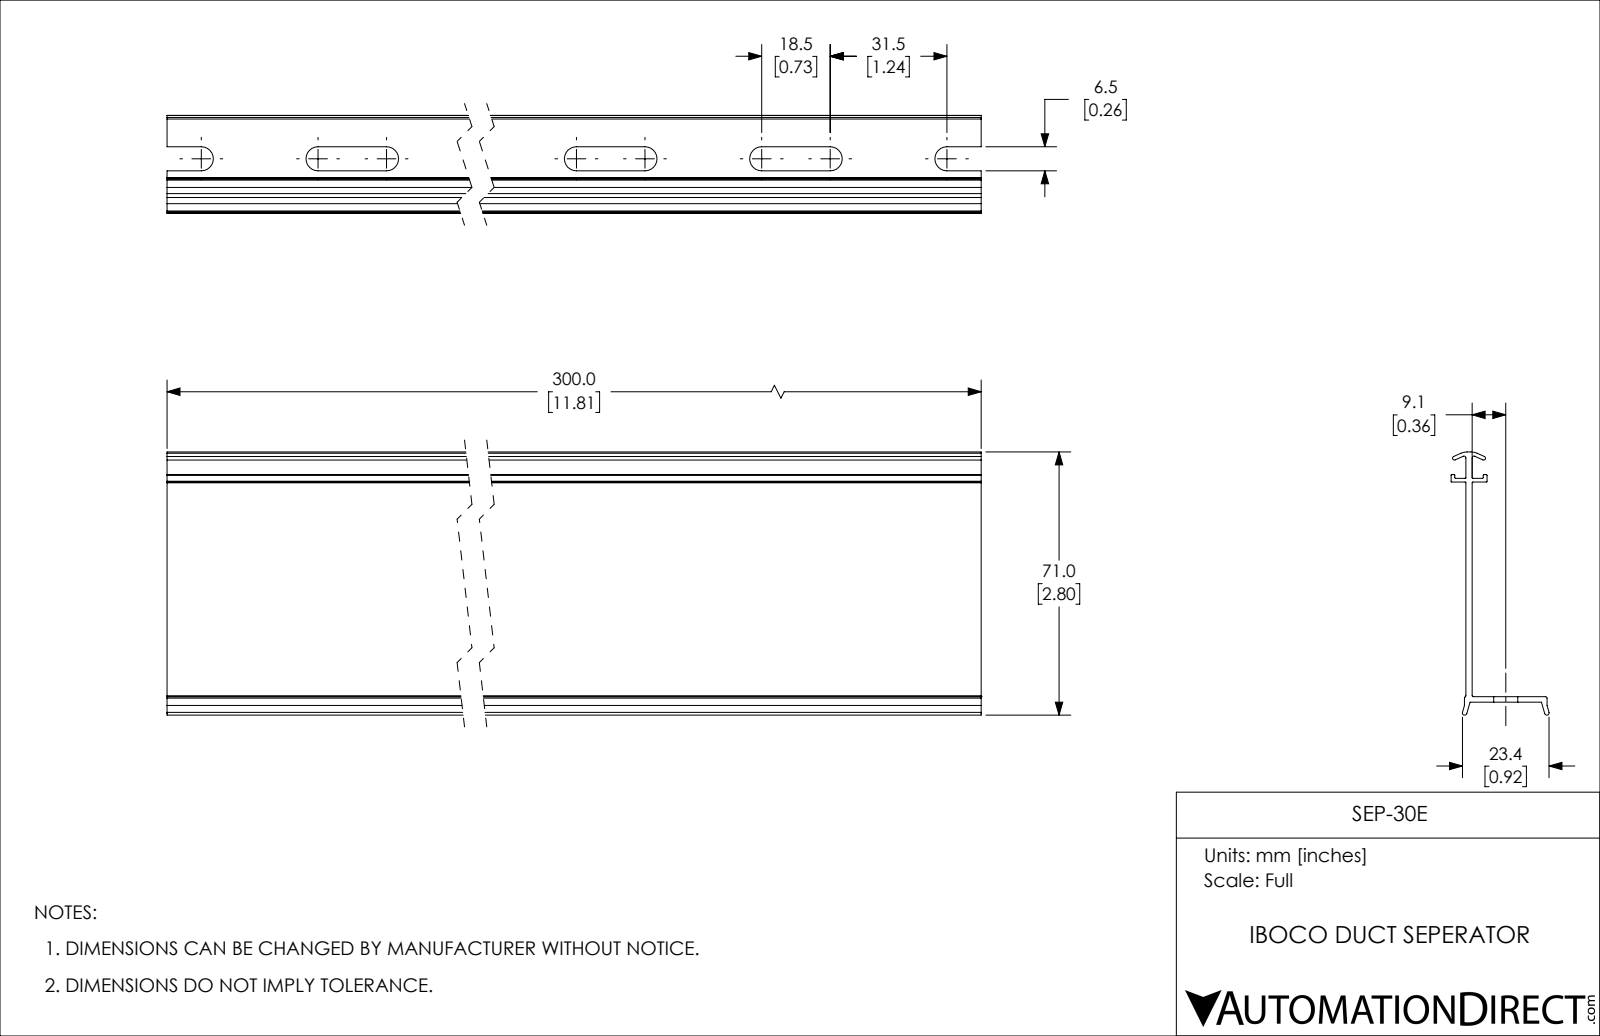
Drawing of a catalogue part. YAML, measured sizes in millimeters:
part_name: "SEP-30E"
step_written_by: "SolidWorks 2019 (CONFIG_CONTROL_DESIGN)"
units: millimeters
bodies: {solids: 1, faces: 86, planar: 45, cylindrical: 17, other: 24}
overall_size: [300, 71, 26.5]
volume: 50160
surface_area: 66390
partial_cylinders:
  - {radius: 3.3, count: 12}
face_to_face_distances: [1.7, 1.5, 1, 59.4, 57.9, 60.4, 58.9, 1.2, 4, 5.7]
